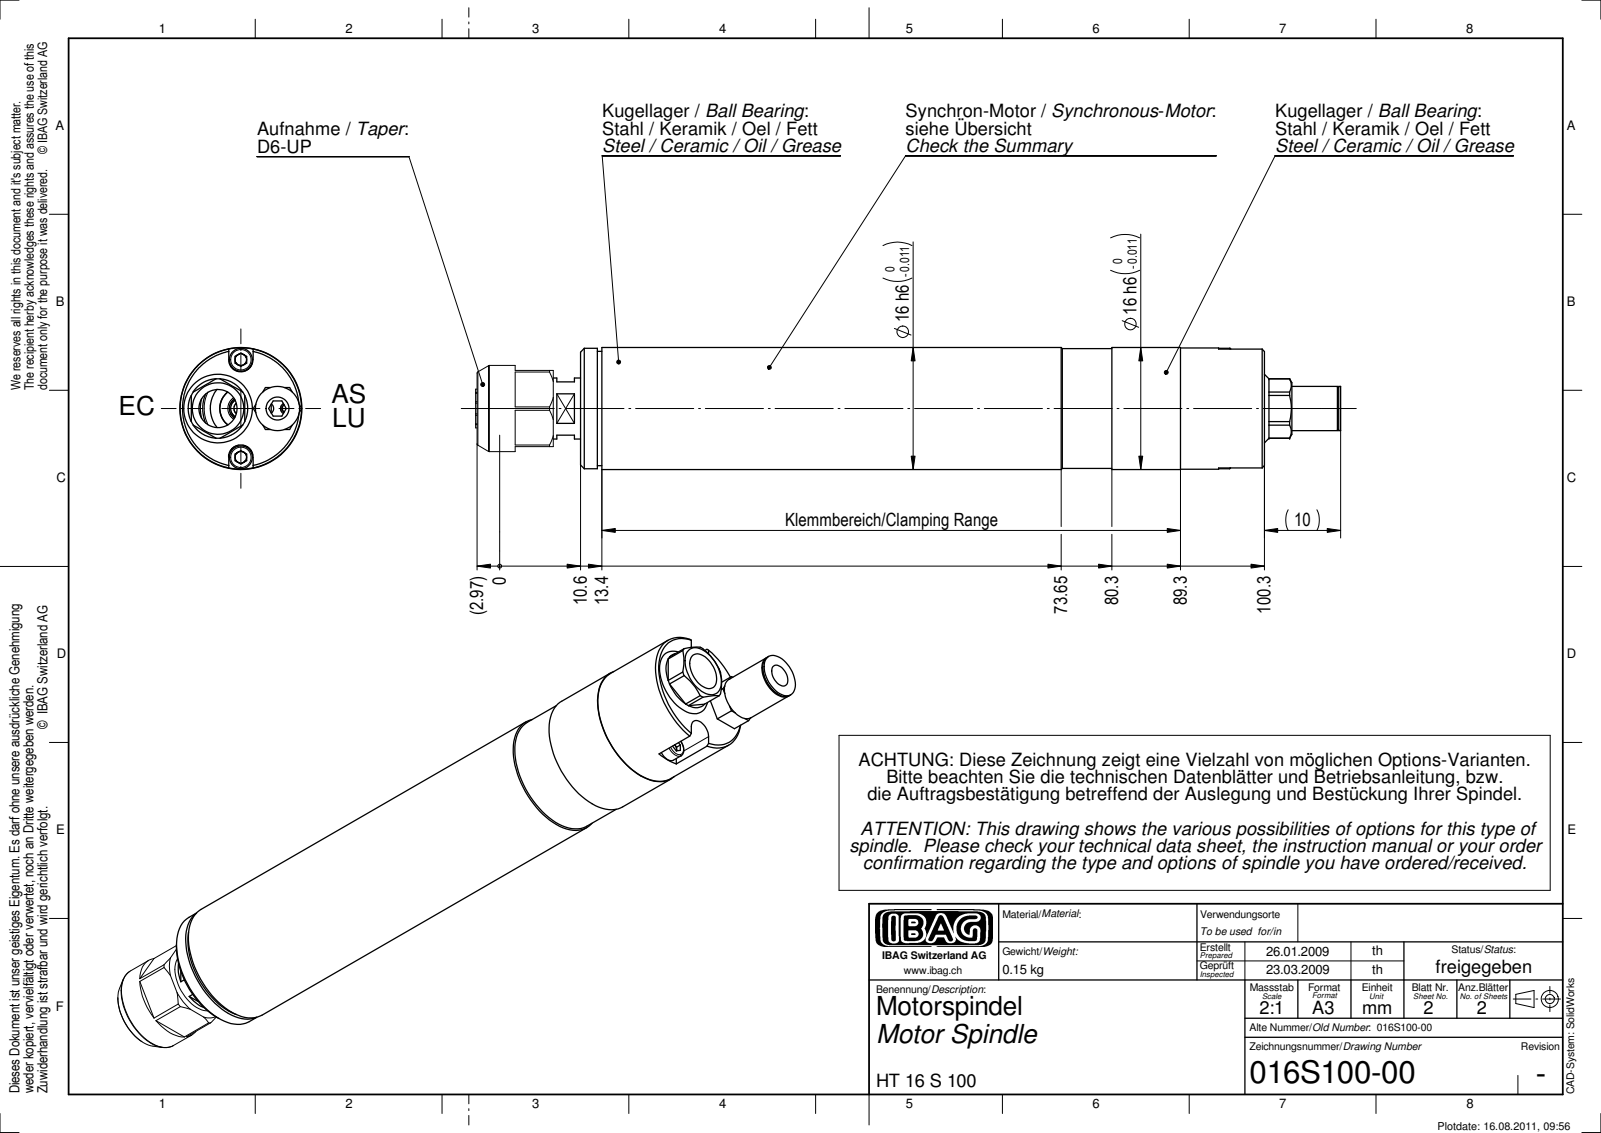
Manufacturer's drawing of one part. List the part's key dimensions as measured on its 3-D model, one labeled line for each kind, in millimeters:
Part name (STEP PRODUCT): 016S100-00
STEP written by: SolidWorks 2010 (CONFIG_CONTROL_DESIGN)
Units: millimetres
Bodies: 0 solids, 211 faces (105 planar, 72 cylindrical, 34 other)
Overall size (bounding box): 113.47 × 16 × 16
Round holes (diameter × count): ⌀1.1 ×4, ⌀0.5 ×1, ⌀3 ×1, ⌀5 ×1, ⌀8.3 ×1
Round bosses / shafts (diameter × count): ⌀3 ×2, ⌀16 ×1, ⌀15.9 ×1, ⌀15.8 ×1, ⌀15.7 ×1, ⌀15 ×1, ⌀11.3 ×1, ⌀9 ×1
Partial cylindrical surfaces — rounded edges, fillets, slot ends (radius × count): R1.6 ×2, R0.75 ×1, R3.9 ×1
Main face-to-face distances: 10, 89.7, 78.7, 11, 103.27, 69.7, 9, 20, 92.27, 1.5
Hole centre spacings: 6.5, 9.19, 7.16, 8.08, 13, 1.7, 3, 3.5
